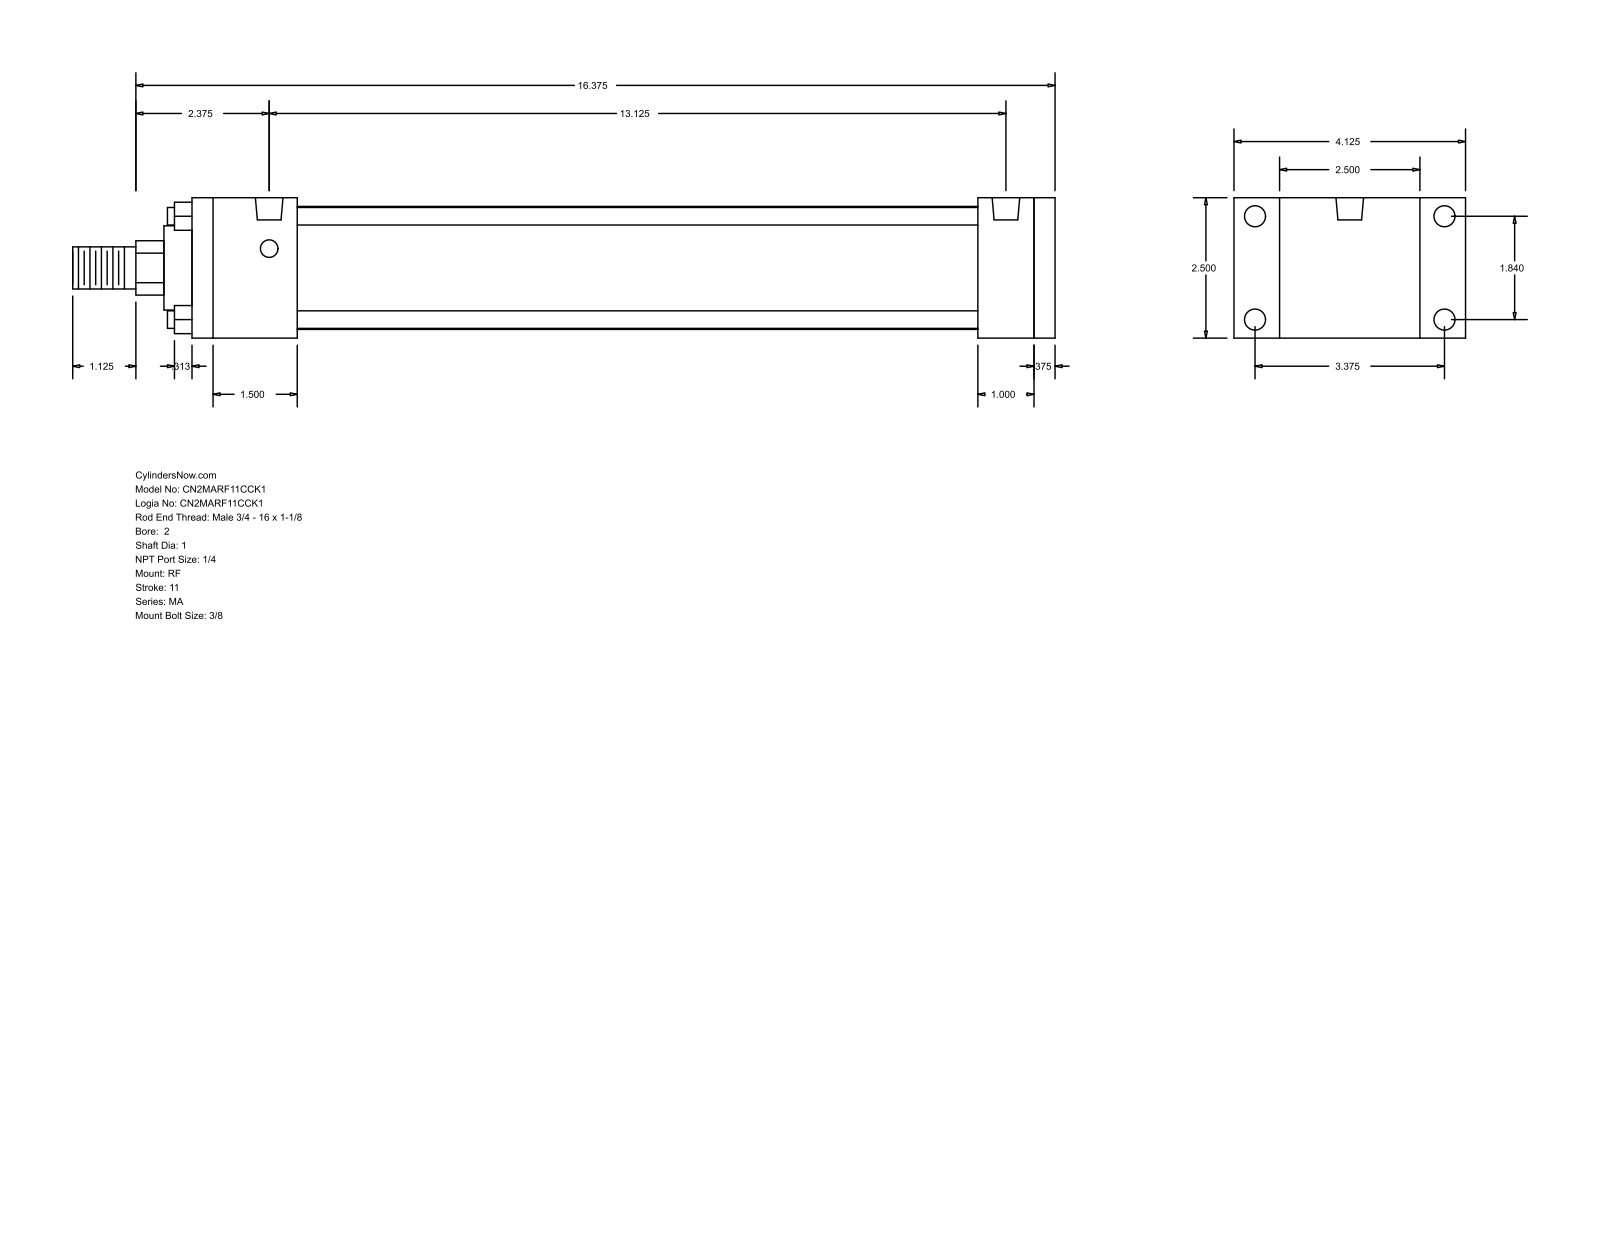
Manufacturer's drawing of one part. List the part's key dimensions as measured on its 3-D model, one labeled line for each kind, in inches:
Part name (STEP PRODUCT): MA_RF__0200_1
STEP written by: GSSL Pune (CONFIG_CONTROL_DESIGN)
Units: inches
Bodies: 0 solids, 92 faces (64 planar, 28 cylindrical, 0 other)
Overall size (bounding box): 17.5 × 4.125 × 2.5
Round holes (diameter × count): ⌀0.313 ×4, ⌀0.375 ×4, ⌀0.492 ×2
Round bosses / shafts (diameter × count): ⌀0.313 ×4, ⌀2.19 ×1, ⌀1.5 ×1, ⌀1 ×1, ⌀0.75 ×1
Partial cylindrical surfaces — rounded edges, fillets, slot ends (radius × count): R0.484 ×1
Main face-to-face distances: 2.5, 15, 0.375, 15.375, 1, 0.813, 0.5, 1.875, 13.125, 13.5
Hole centre spacings: 1.84, 3.375, 3.844, 13.125
